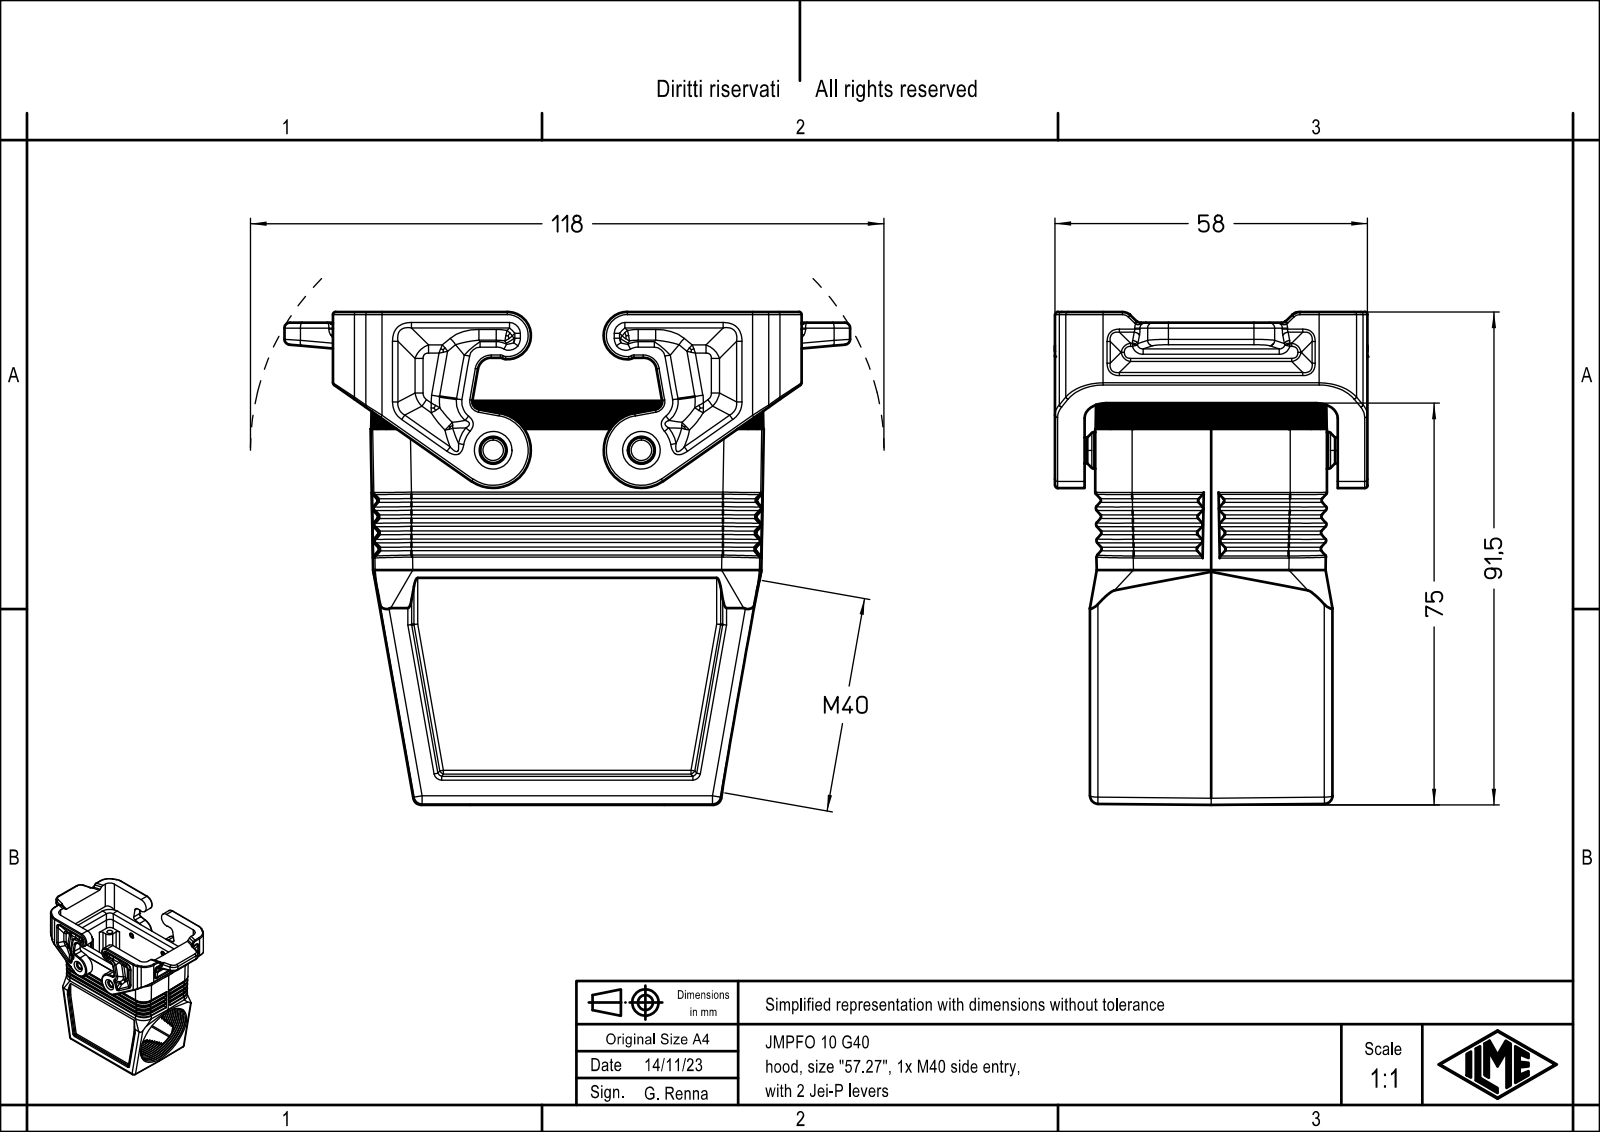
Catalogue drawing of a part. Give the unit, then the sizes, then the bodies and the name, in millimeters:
Units: millimetres
Overall size (bounding box): 105 × 91.45 × 58.08
Round holes (diameter × count): ⌀3 ×4, ⌀3.5 ×4, ⌀4.8 ×2, ⌀38.6 ×1
Round bosses / shafts (diameter × count): ⌀6.8 ×2
Partial cylindrical surfaces — rounded edges, fillets, slot ends (radius × count): R0.5 ×69, R1 ×56, R3 ×34, R1.5 ×28, R2 ×20, R0.33 ×15, R7 ×14, R4 ×12
Main face-to-face distances: 39.25, 2, 3.75, 5.75, 45, 1, 41.25, 43, 4.75, 40.25
Hole centre spacings: 27, 57, 63.07, 27.5
Volume: 91 606 mm³ · Surface area: 47 200 mm²
Bodies: 1 solid, 1102 faces (274 planar, 350 cylindrical, 478 other)
Part name (STEP PRODUCT): JMPFO 10 G40
STEP written by: Creo Elements/Direct Modeling 20.1B 02-Apr-2019 (C) Parametric Technology GmbH (AUTOMOTIVE_DESIGN)
